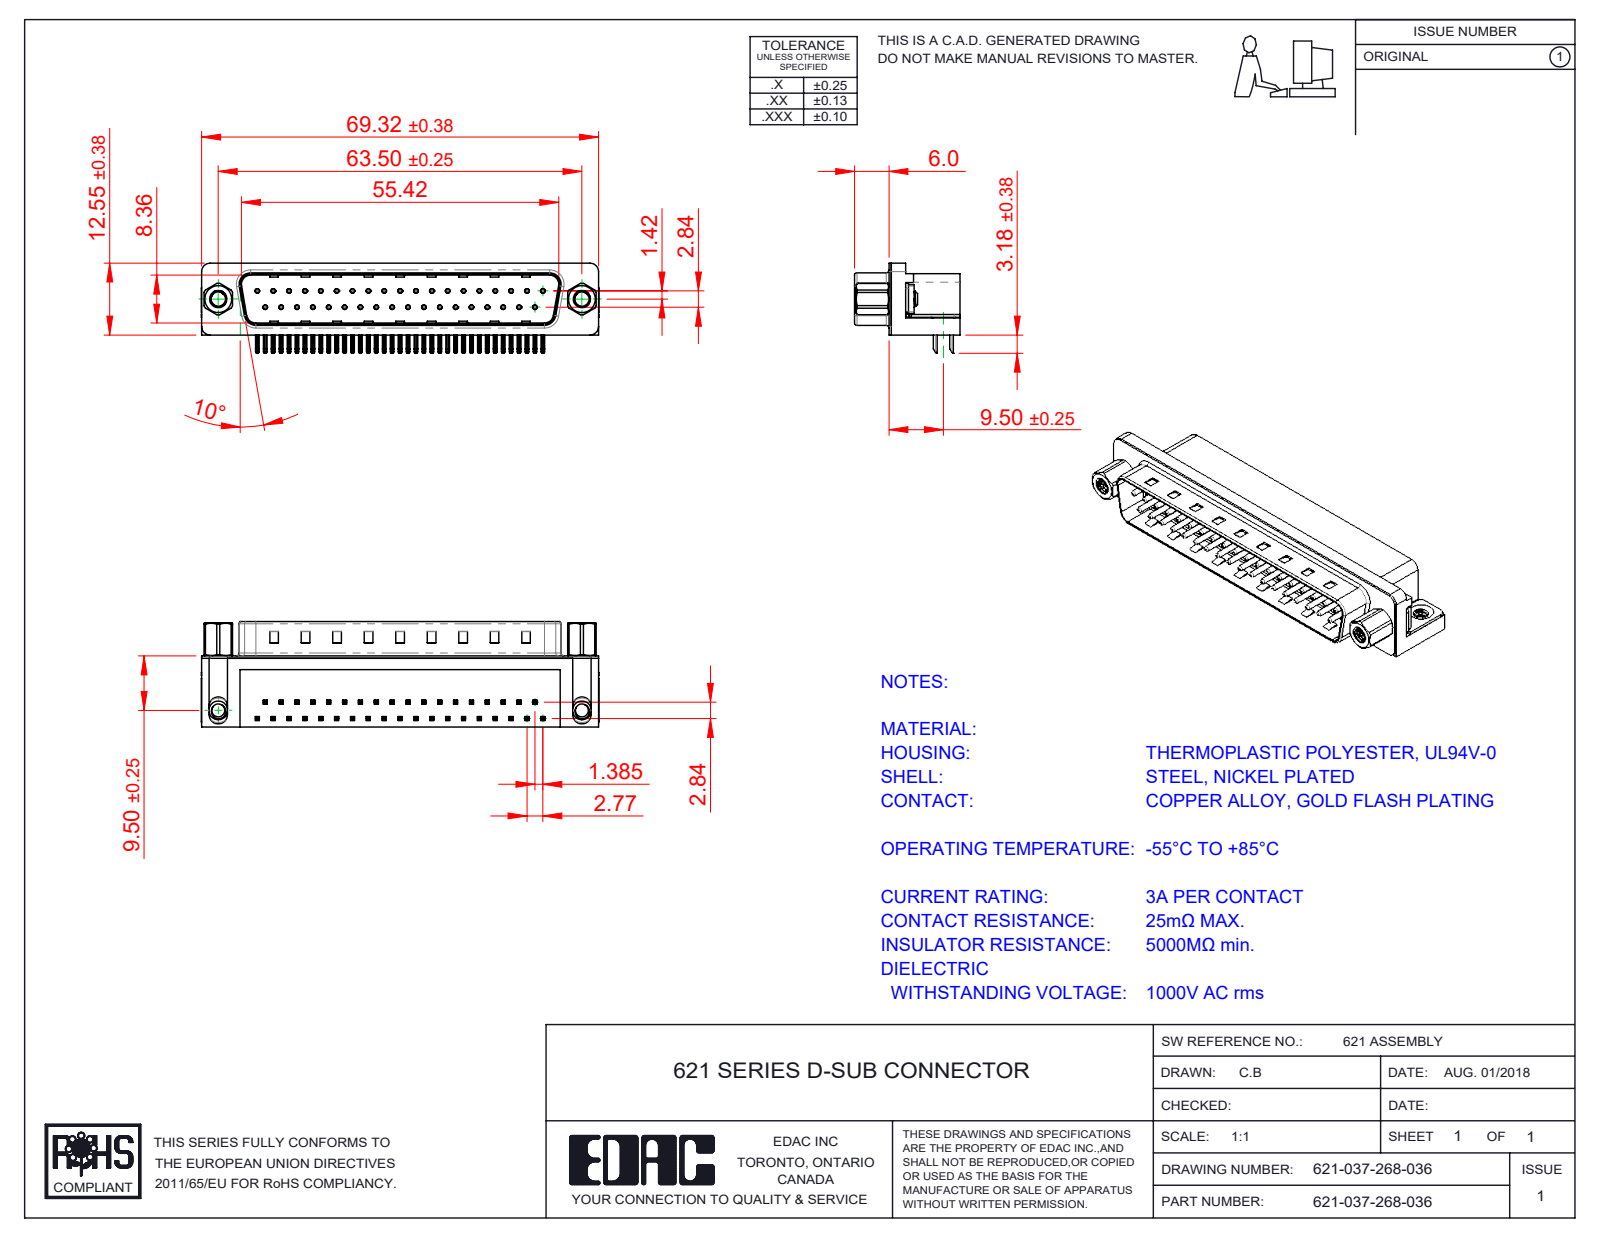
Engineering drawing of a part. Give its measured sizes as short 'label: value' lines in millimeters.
name: 621 M3 Hex Standoff 5; 621 M3 Threaded Rivet; 621 2 Prong Board Lock; 621-037-268-036 (+4 more)
written by: SolidWorks 2016 (CONFIG_CONTROL_DESIGN)
unit: mm
bodies: 45 solids, 3387 faces (2067 planar, 1019 cylindrical, 301 other)
size: 69.4 × 18.4 × 16.25
volume: 8 860 mm³; area: 10 632 mm²
holes: 37× ⌀0.35, 37× ⌀0.8, 2× ⌀2.5, 2× ⌀4, 2× ⌀4.8, 2× ⌀5
bosses: 37× ⌀0.75, 2× ⌀4.9, 2× ⌀4.75, 2× ⌀3.9, 2× ⌀3
rounds: 156× R0.25, 74× R0.12, 16× R1, 14× R0.5, 8× R1.6, 7× R1.5, 4× R0.32, 4× R0.9
face distances: 0.4, 12, 10.35, 8.76, 1.7, 2.1, 10.46, 10.86, 9, 12.4
hole spacings: 3.16, 2.77, 5.54, 8.31, 11.08, 13.85, 19.39, 22.16
